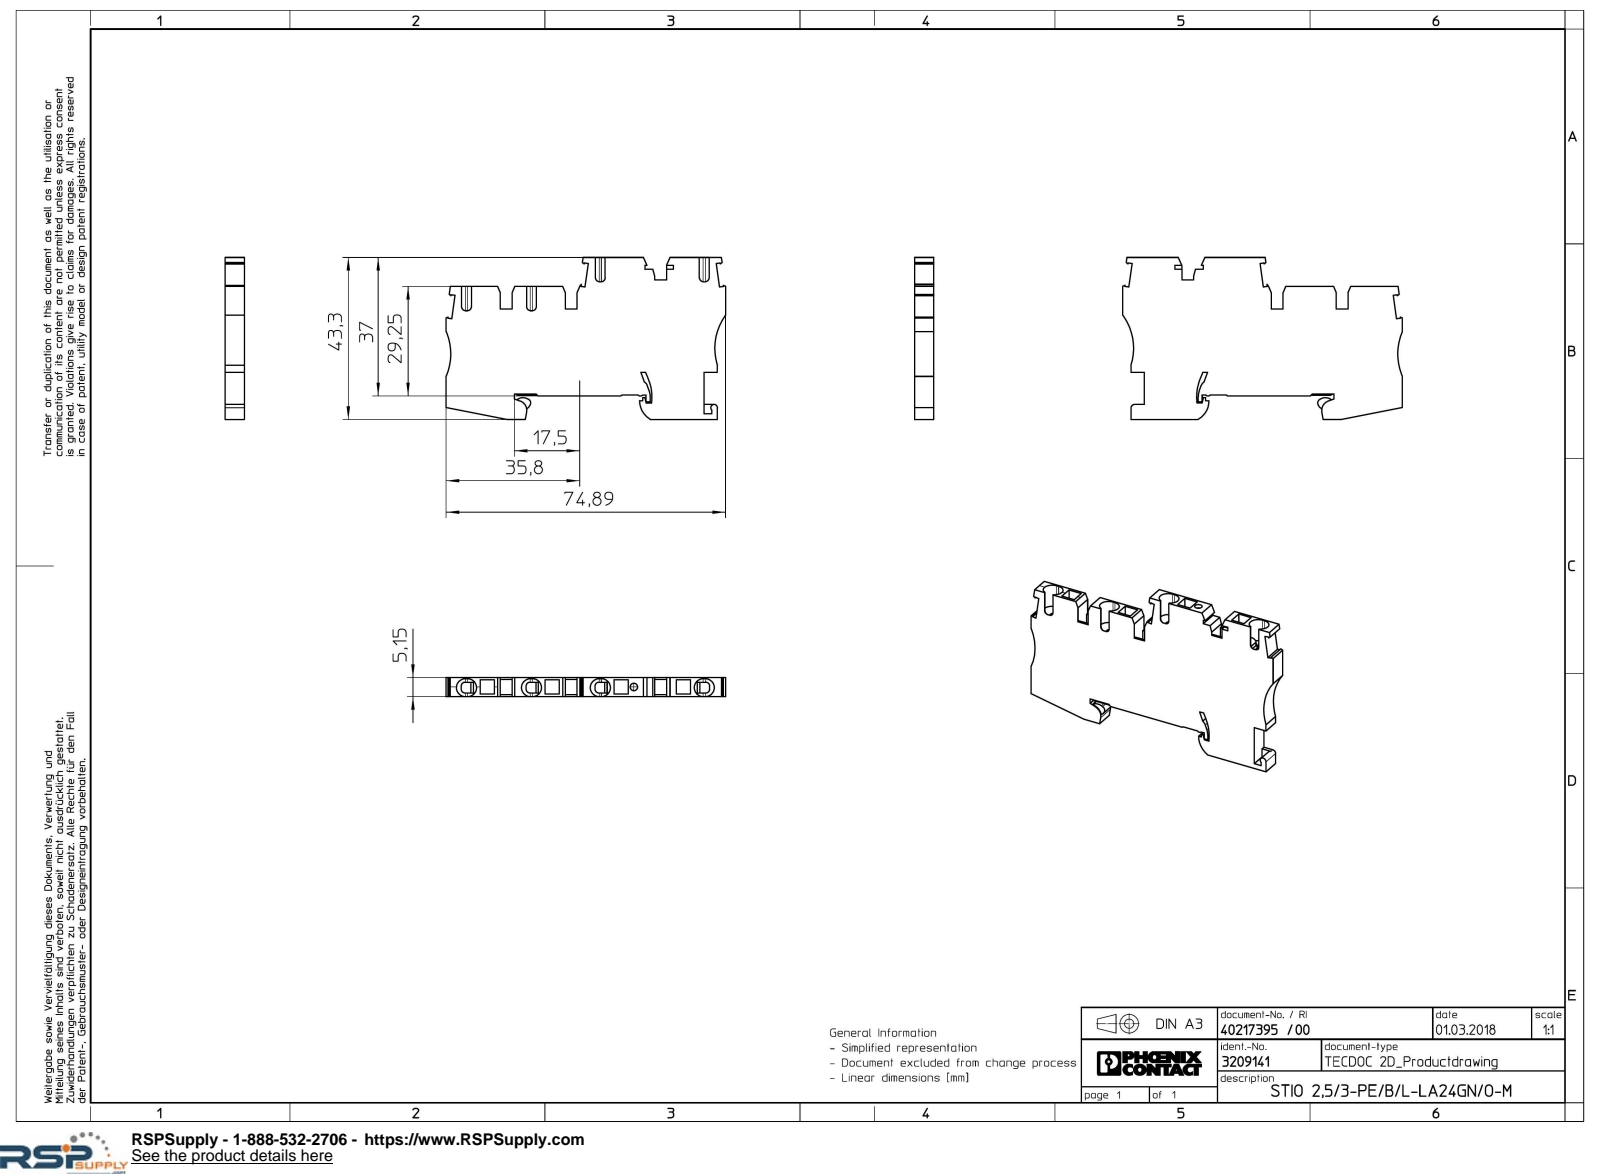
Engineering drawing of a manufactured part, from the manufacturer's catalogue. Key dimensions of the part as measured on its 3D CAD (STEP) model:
Part name (STEP PRODUCT): STIO_2.5_3-PE_B_L-LA24GN_O-M-SELECT
STEP written by: Creo Elements/Direct Modeling 18.1I 14-Aug-2016 (C) Parametric Technology GmbH (AUTOMOTIVE_DESIGN)
Units: millimetres
Bodies: 1 solid, 240 faces (191 planar, 37 cylindrical, 12 other)
Overall size (bounding box): 74.89 × 43.3 × 5.15
Volume: 11 262 mm³ · Surface area: 8 345 mm²
Round holes (diameter × count): ⌀2 ×1
Partial cylindrical surfaces — rounded edges, fillets, slot ends (radius × count): R1 ×16, R2.4 ×8, R2.6 ×2, R15 ×2, R0.9 ×1, R1.1 ×1, R2 ×1, R5 ×1
Main face-to-face distances: 5.15, 3.15, 17.4, 0.65, 6.3, 4.57, 3.8, 4.58, 0.57, 23.96
